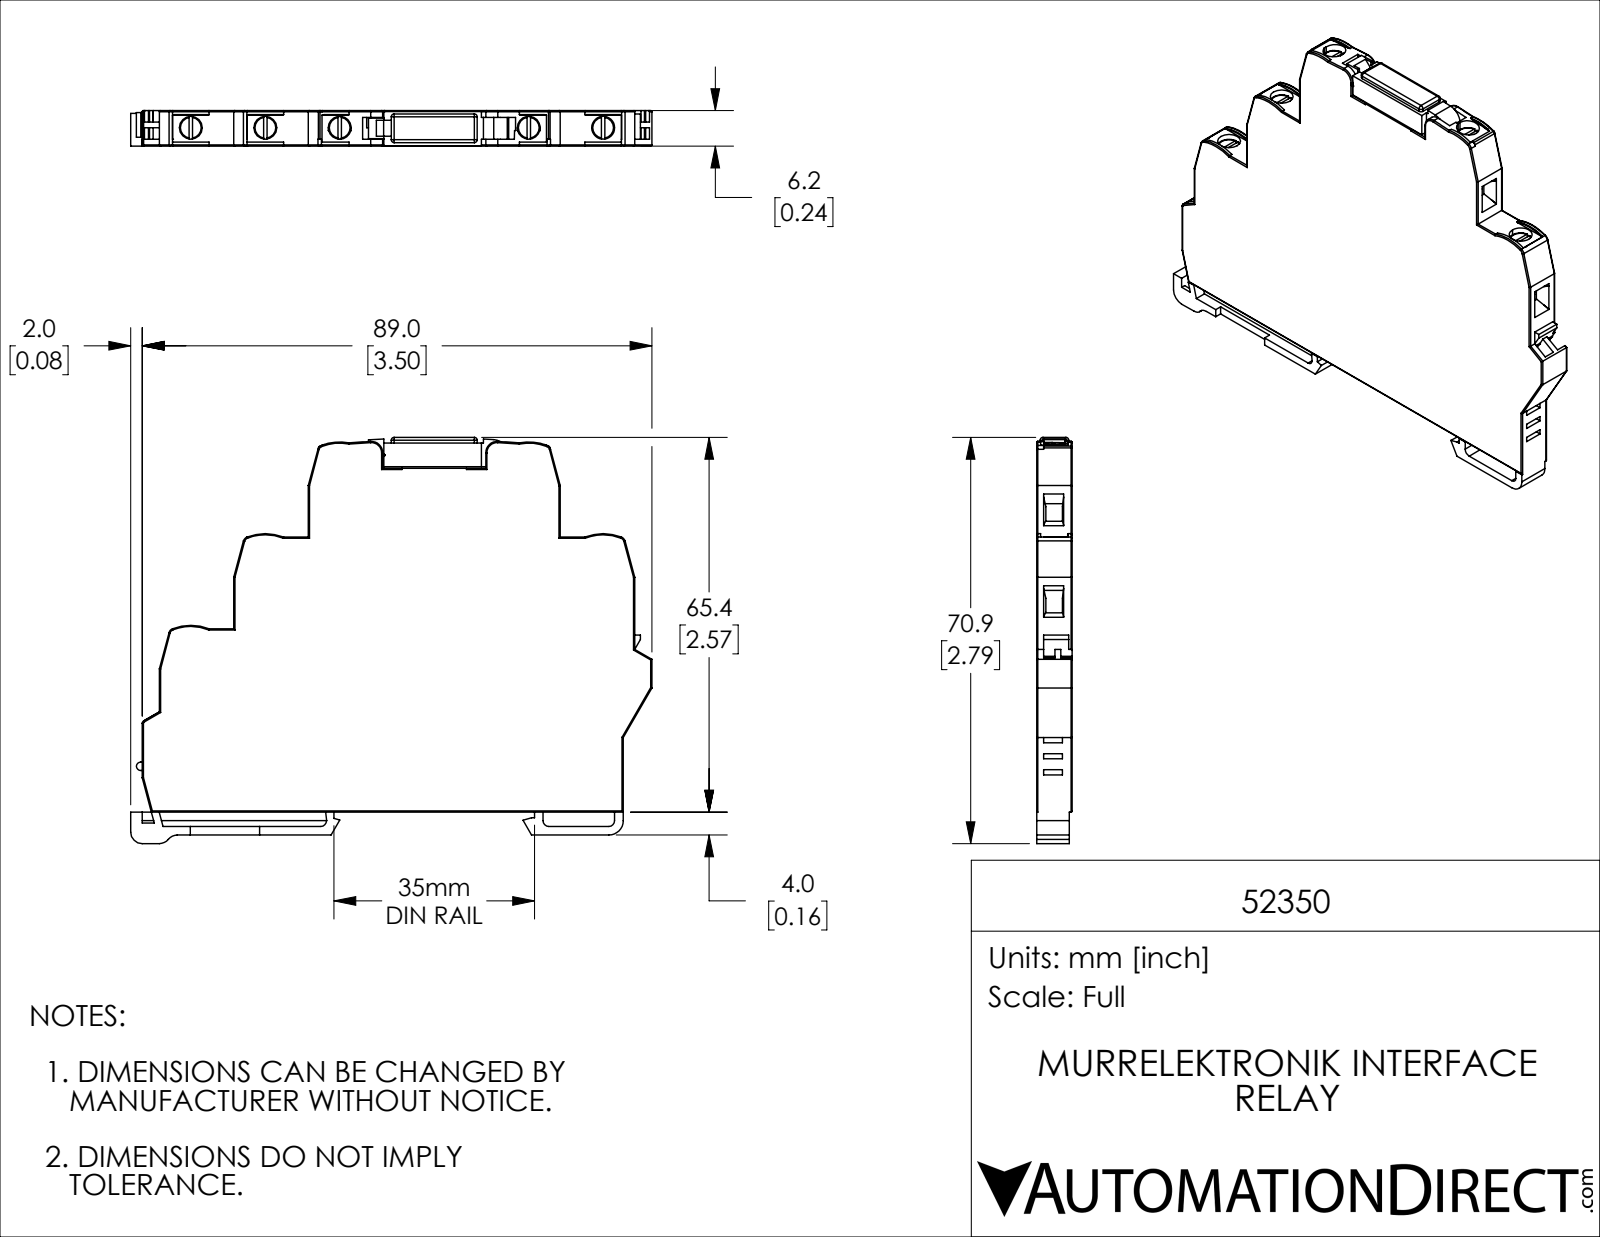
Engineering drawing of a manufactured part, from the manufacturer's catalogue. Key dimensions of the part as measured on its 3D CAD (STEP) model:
Part name (STEP PRODUCT): 52350
STEP written by: SolidWorks 2019 (CONFIG_CONTROL_DESIGN)
Units: inches
Bodies: 2 solids, 566 faces (351 planar, 147 cylindrical, 68 other)
Overall size (bounding box): 3.583 × 2.791 × 0.244
Volume: 1.706 in³ · Surface area: 20.13 in²
Round holes (diameter × count): ⌀0.157 ×5, ⌀0.075 ×1
Round bosses / shafts (diameter × count): ⌀0.079 ×1
Partial cylindrical surfaces — rounded edges, fillets, slot ends (radius × count): R0.008 ×56, R0.02 ×11, R0.039 ×8, R0.079 ×6, R0.03 ×5, R0.346 ×5, R0.005 ×4, R0.016 ×3
Main face-to-face distances: 0.244, 0.059, 0.197, 0.098, 0.157, 0.118, 0.047, 0.02, 0.039, 2.362
Hole centre spacings: 0.512, 1.811, 2.323, 1.024, 1.299, 2.835
